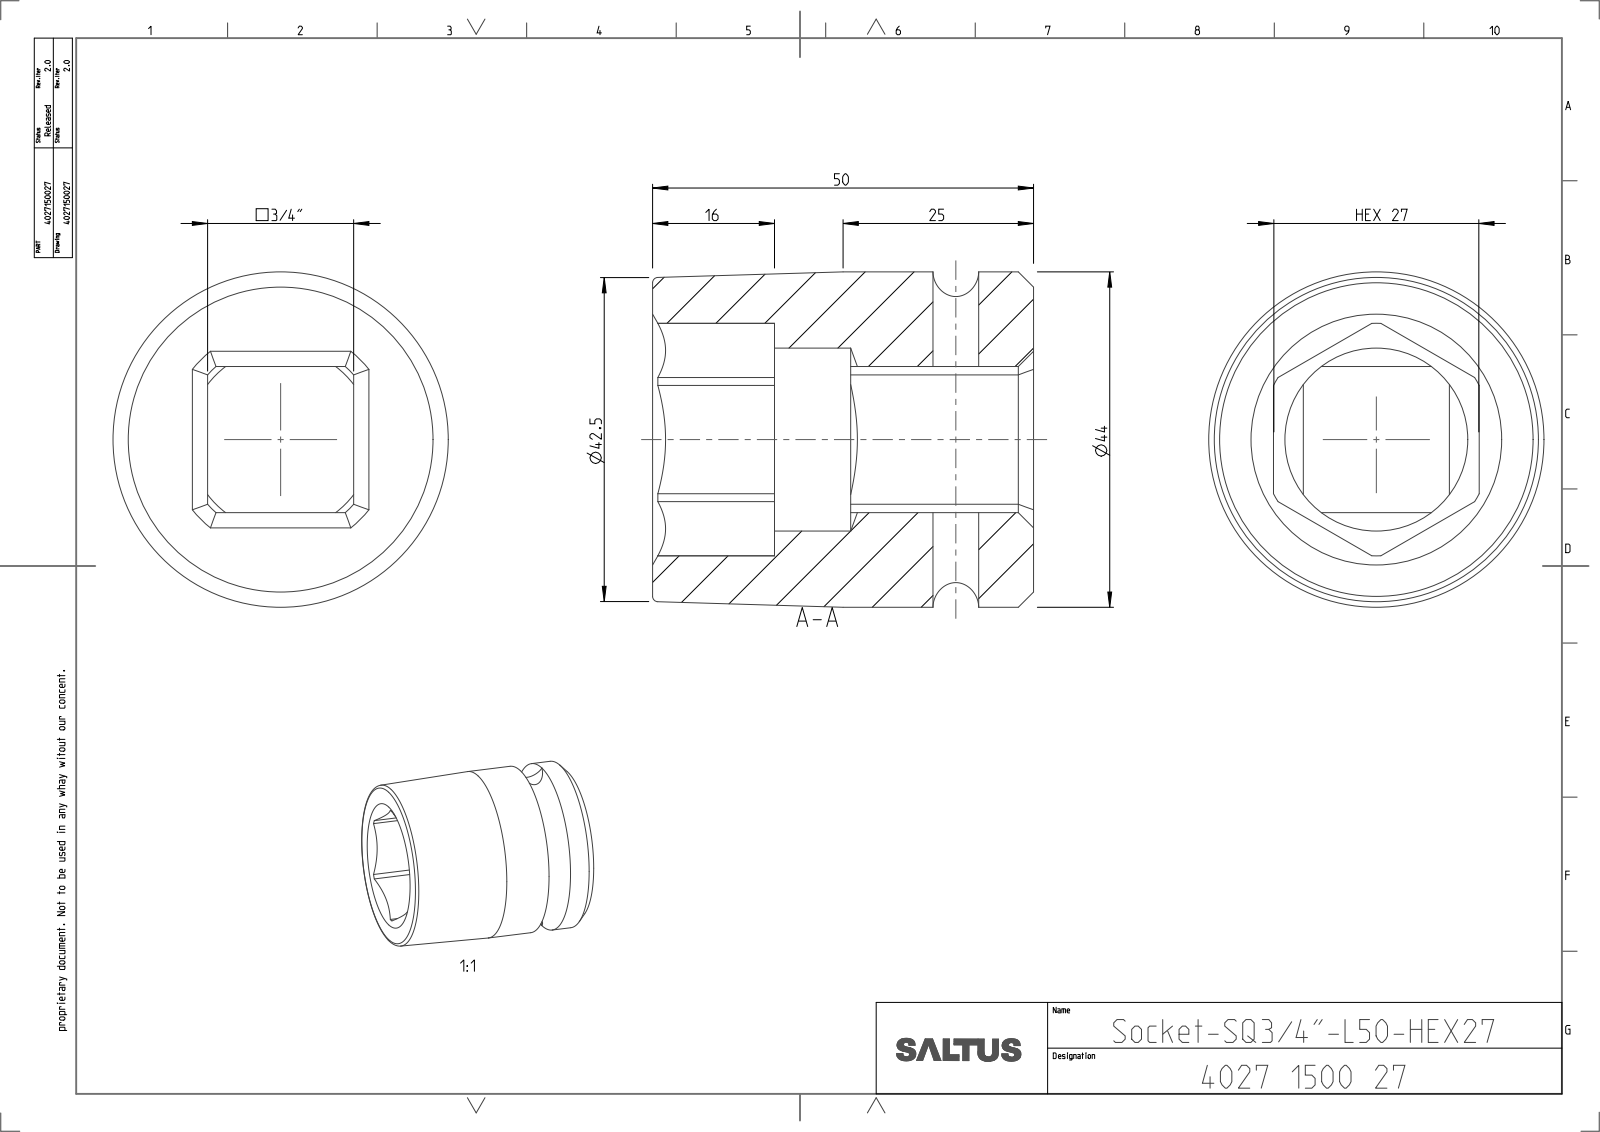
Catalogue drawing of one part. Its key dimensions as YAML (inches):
part_name: "4027150027"
step_written_by: "CREO PARAMETRIC BY PTC INC, 2022414 (CONFIG_CONTROL_DESIGN)"
units: inches
bodies: {solids: 1, faces: 59, planar: 21, cylindrical: 20, other: 18}
overall_size: [1.969, 1.732, 1.732]
volume: 2.951
surface_area: 20.64
round_holes:
  - {diameter: 0.236, count: 1}
  - {diameter: 0.945, count: 1}
round_bosses_or_shafts:
  - {diameter: 1.732, count: 1}
partial_cylinders:
  - {radius: 0.504, count: 1}
  - {radius: 0.601, count: 1}
face_to_face_distances: [0.755, 1.063, 1.969, 0.154, 0.909, 1.339, 0.63, 0.945, 0.394, 1.024]
